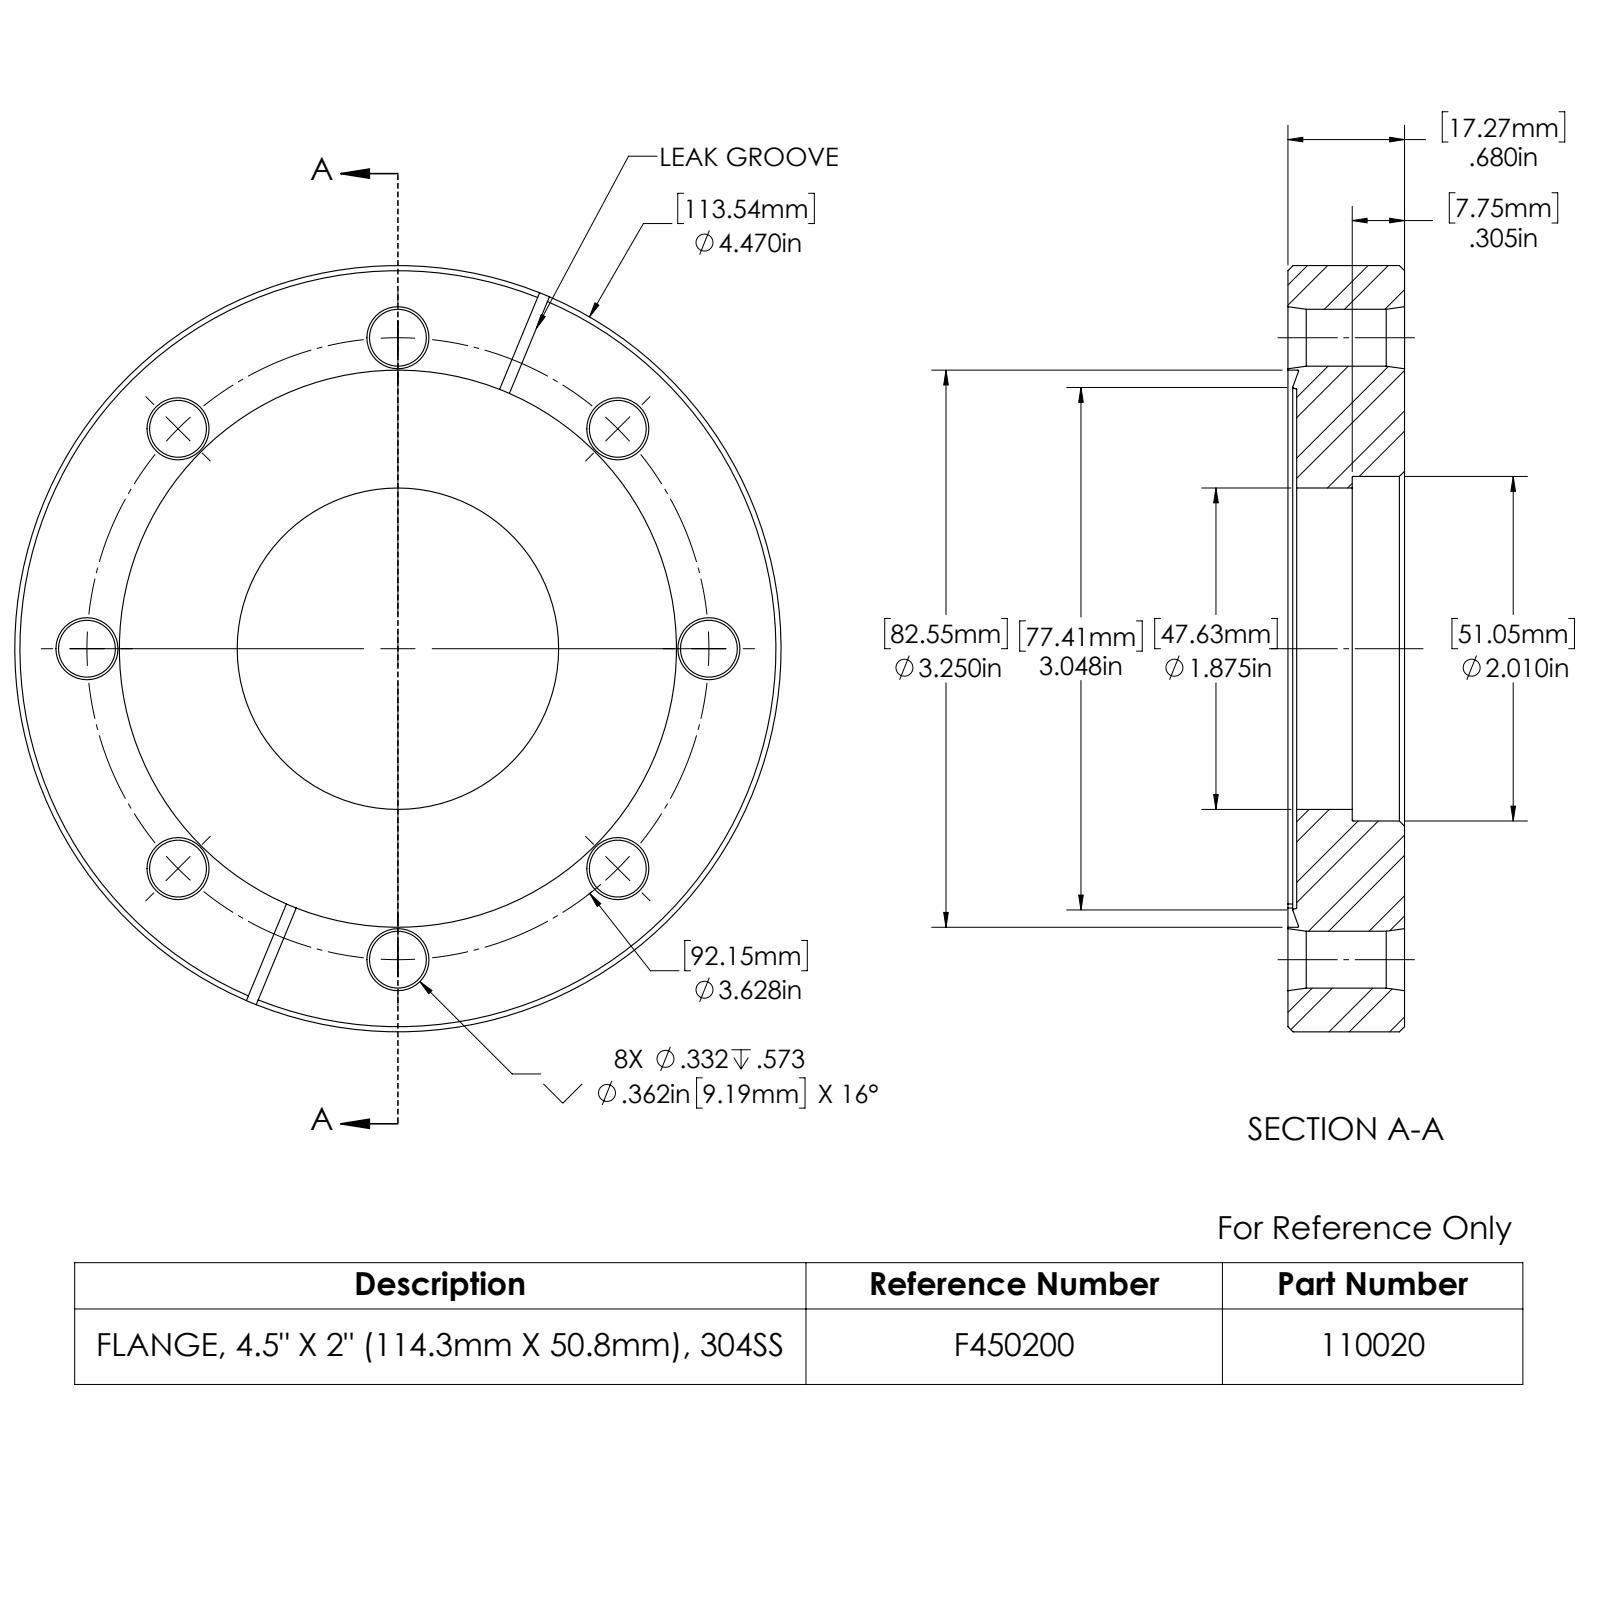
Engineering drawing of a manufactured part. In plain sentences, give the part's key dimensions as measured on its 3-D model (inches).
The part is named "110020_A". Its 3-D file was written by "SolidWorks 2022 (CONFIG_CONTROL_DESIGN)". It is 1 solid with 86 faces: 11 planar, 24 cylindrical and 51 other. Overall it measures 4.47 by 4.47 by 0.68 inches. Its volume is 7.888 cubic inches and its surface area 43.7 square inches. Round holes: 8 of diameter 0.332, 1 of diameter 1.875, 1 of diameter 2.01, 1 of diameter 3.25. Round bosses or shafts: 1 of diameter 4.47. The main face-to-face distances are 0.68, 0.051, 0.629, 0.375, 0.324, 0.305, 0.052, 0.323, 0.628, 0.063. The hole center spacings are 1.389, 1.814, 3.352, 2.565, 2.566, 3.628, 3.628.
